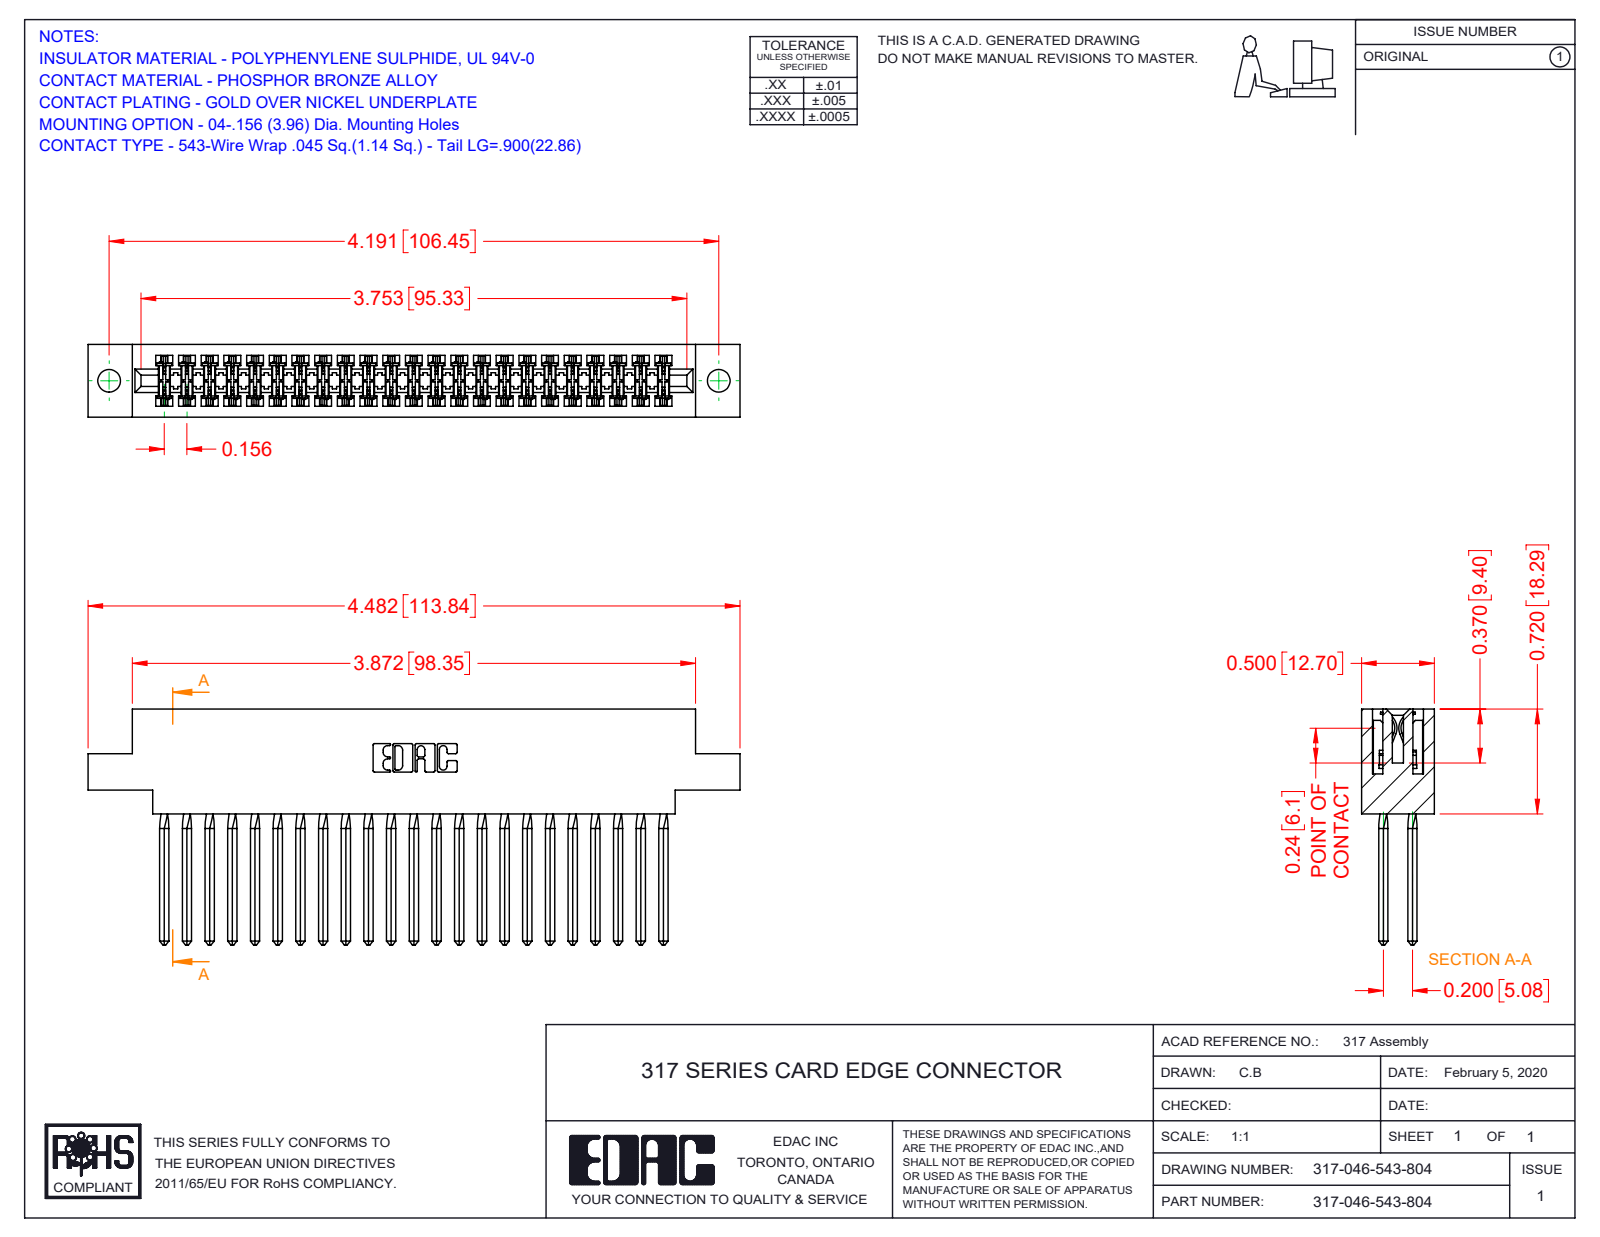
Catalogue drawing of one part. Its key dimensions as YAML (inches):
part_name: "317 Part_.156 Dia - TH; 317-290-001_543; 317-046-543-804"
step_written_by: "SolidWorks 2016 (CONFIG_CONTROL_DESIGN)"
units: inches
bodies: {solids: 47, faces: 4196, planar: 3416, cylindrical: 596, other: 184}
overall_size: [4.482, 1.62, 0.5]
volume: 1.135
surface_area: 42.32
round_holes:
  - {diameter: 0.156, count: 2}
partial_cylinders:
  - {radius: 0.015, count: 92}
  - {radius: 0.01, count: 22}
  - {radius: 0.007, count: 6}
  - {radius: 0.031, count: 6}
  - {radius: 0.026, count: 3}
  - {radius: 0.095, count: 2}
  - {radius: 0.1, count: 2}
  - {radius: 0.11, count: 2}
face_to_face_distances: [0.5, 0.075, 0.425, 0.11, 0.35, 0.195, 0.22, 0.094, 0.72, 0.2]
hole_center_spacings: [4.191]
